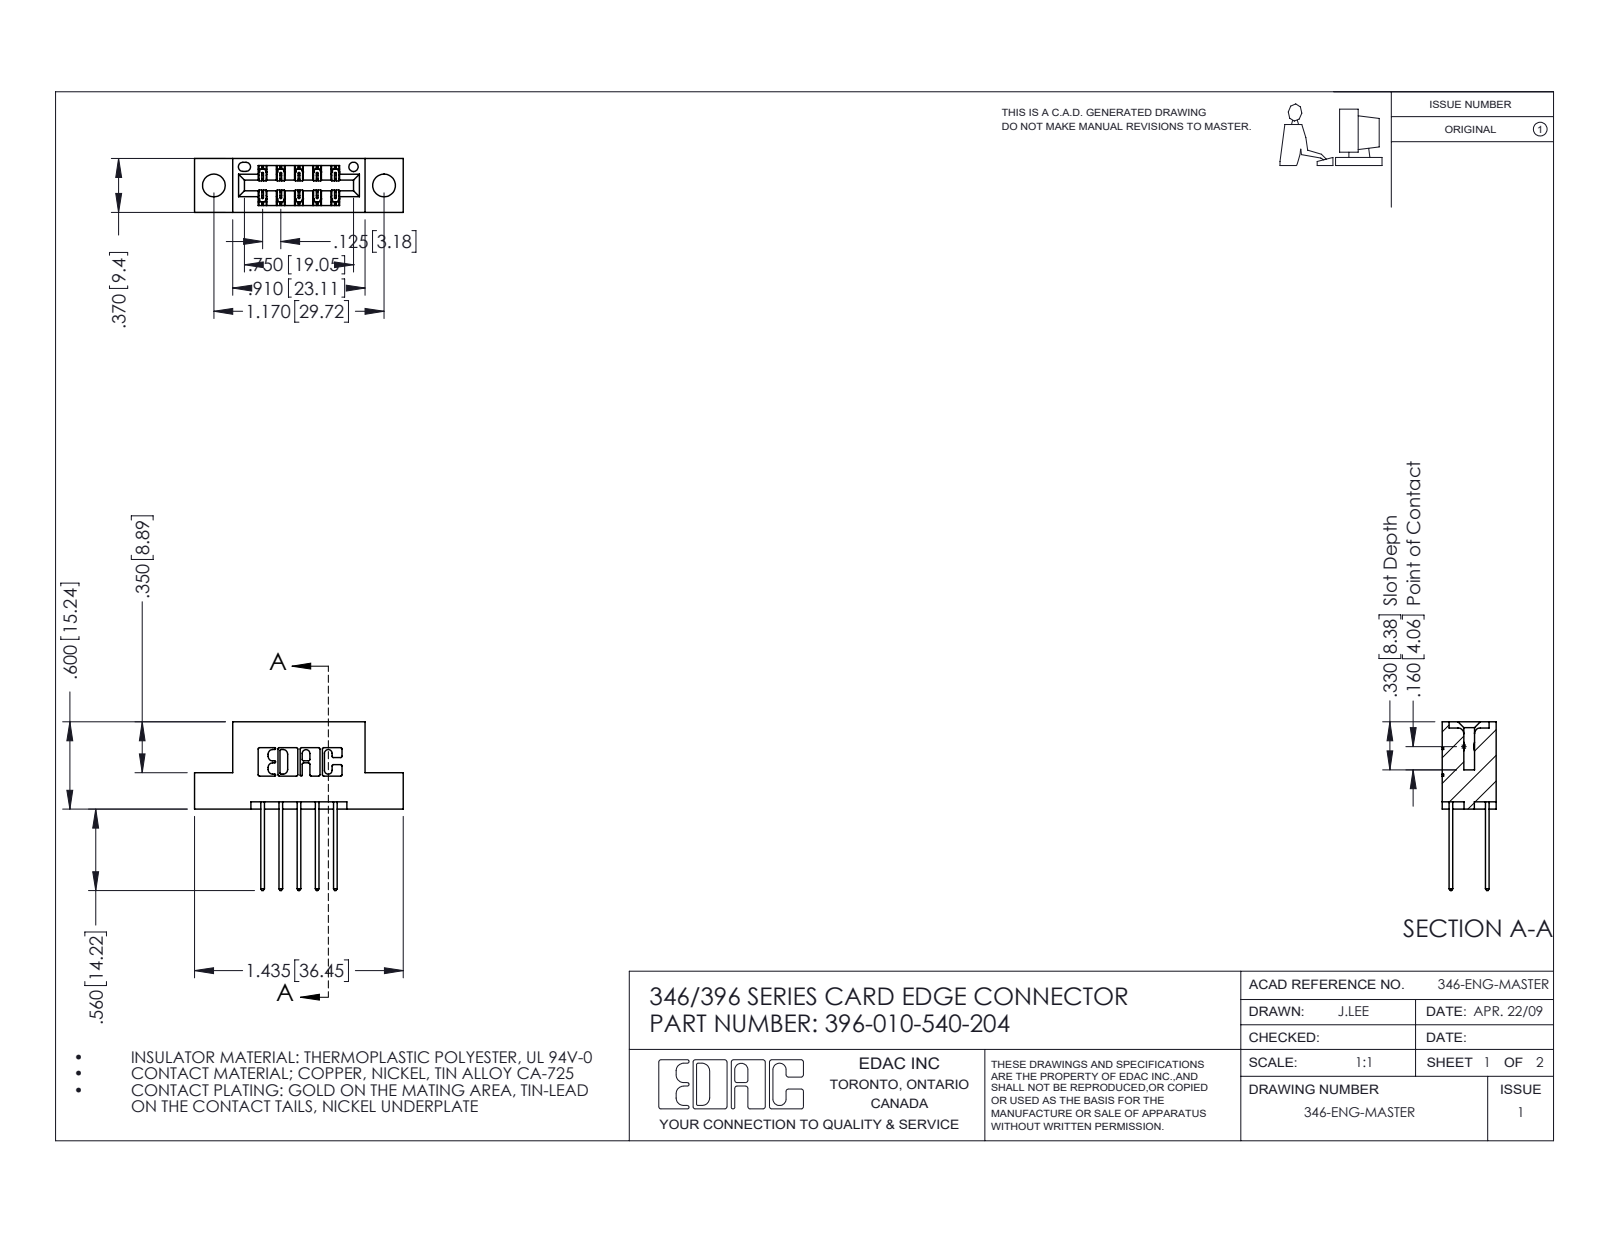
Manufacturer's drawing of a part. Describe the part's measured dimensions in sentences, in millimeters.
The part is named "345-292-001_345-293-140; 346 Part_Flush Mounting Lugs - 0.156 Dia-TH; 396-010-540-204". Its 3-D file was written by "SolidWorks 2016 (CONFIG_CONTROL_DESIGN)". It is 11 solids with 642 faces: 426 planar, 216 cylindrical and 0 other. Overall it measures 36.4 by 29.5 by 9.4 millimeters. Its volume is 3 210 cubic millimeters and its surface area 3 833 square millimeters. Round holes: 2 of diameter 4, 1 of diameter 1.6. Partial cylindrical surfaces (rounded edges, fillets, slot ends): 22 of radius 0.3, 15 of radius 0.2, 10 of radius 0.3, 6 of radius 0.2, 6 of radius 0.8, 3 of radius 0.7, 2 of radius 0.4, 2 of radius 0.6. The main face-to-face distances are 6.4, 1.2, 8.2, 9.4, 0.6, 1.8, 7.6, 7, 3.2, 3.2. The hole center spacings are 6.2, 24.6, 29.7.
